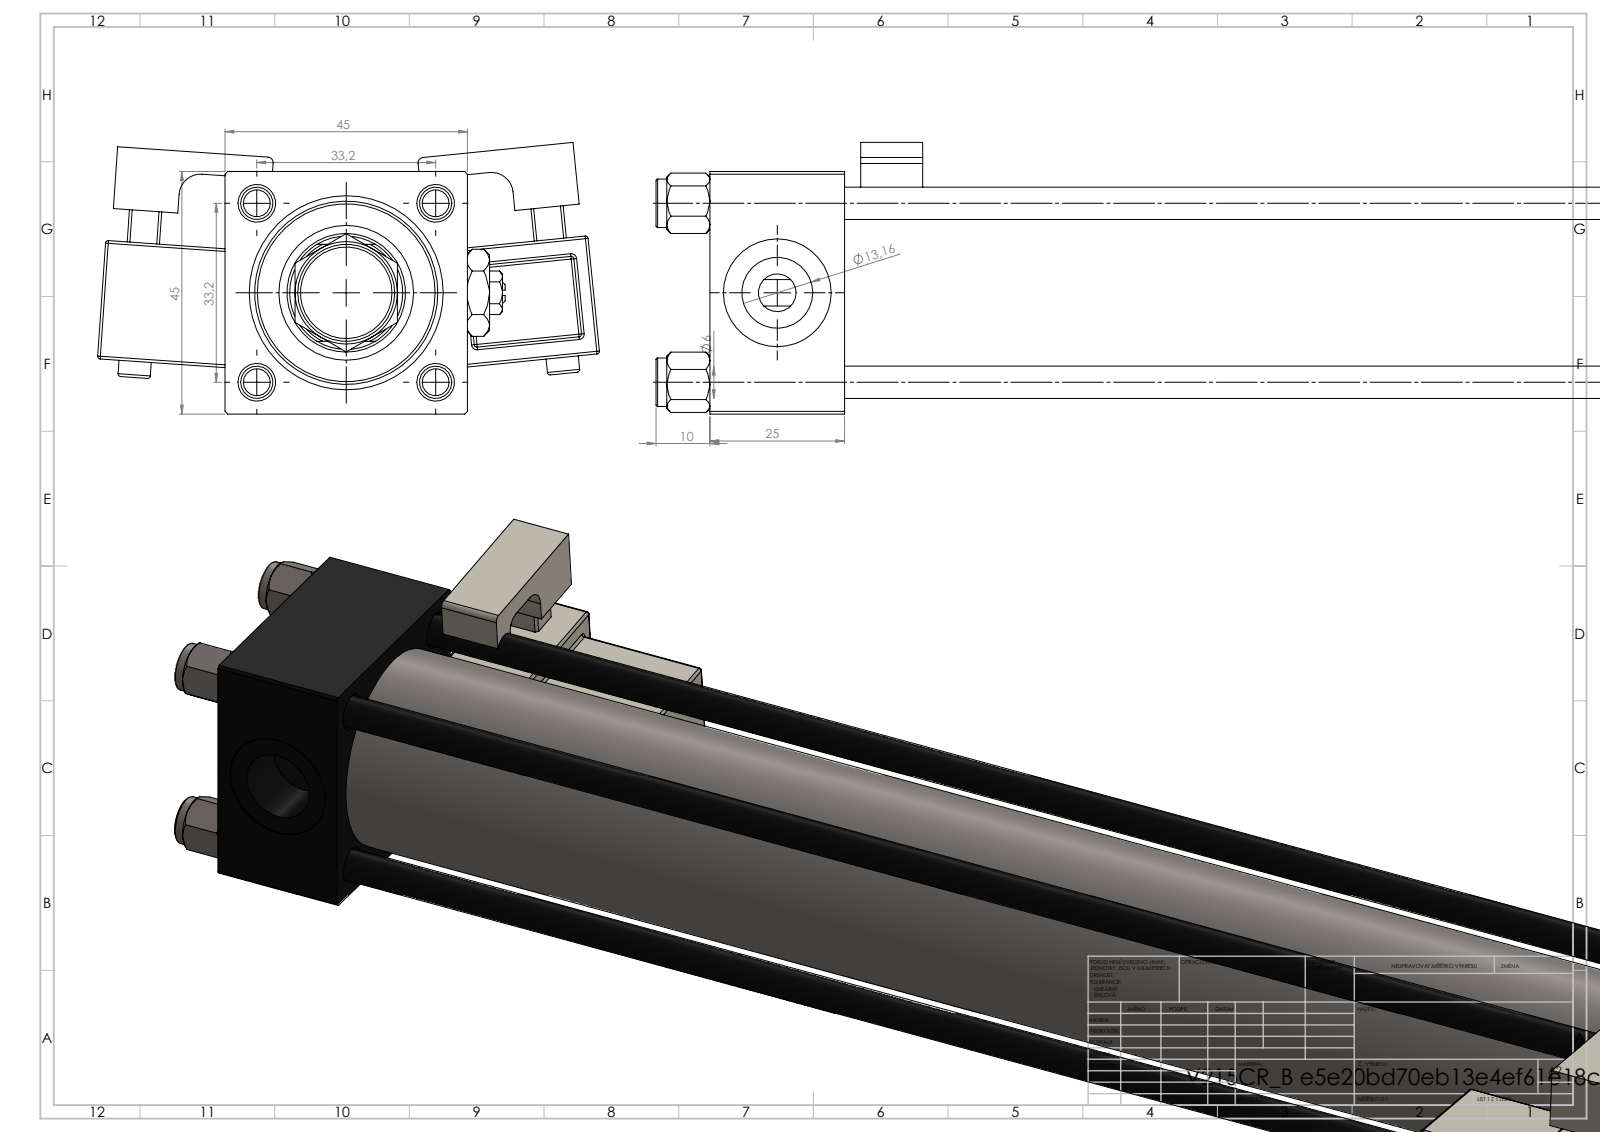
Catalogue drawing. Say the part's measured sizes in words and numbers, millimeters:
The part is named "MFA; V215CR_MSU; Zatka_pro_OIL_PORT; NUT_M5_B (+4 more)". Its 3-D file was written by "SolidWorks 2019 (CONFIG_CONTROL_DESIGN)". It is 16 solids with 1466 faces: 556 planar, 152 cylindrical and 758 other. Overall it measures 421 by 93.14 by 50.4 millimeters. Its volume is 450 818 cubic millimeters and its surface area 177 145 square millimeters. Round holes: 4 of diameter 6, 2 of diameter 7, 2 of diameter 13.16, 2 of diameter 20, 1 of diameter 10.5, 1 of diameter 22, 1 of diameter 24, 1 of diameter 25, 1 of diameter 32, 1 of diameter 33. Round bosses or shafts: 4 of diameter 9, 2 of diameter 6, 1 of diameter 38, 1 of diameter 34, 1 of diameter 18, 1 of diameter 11. Partial cylindrical surfaces (rounded edges, fillets, slot ends): 48 of radius 0.5, 2 of radius 1, 2 of radius 2.5, 2 of radius 4, 1 of radius 10.5. The main face-to-face distances are 45, 25, 305, 280, 353, 3, 262.5, 17.5, 44.8, 39.5. The hole center spacings are 23.48, 33.2, 46.95, 305.5.
